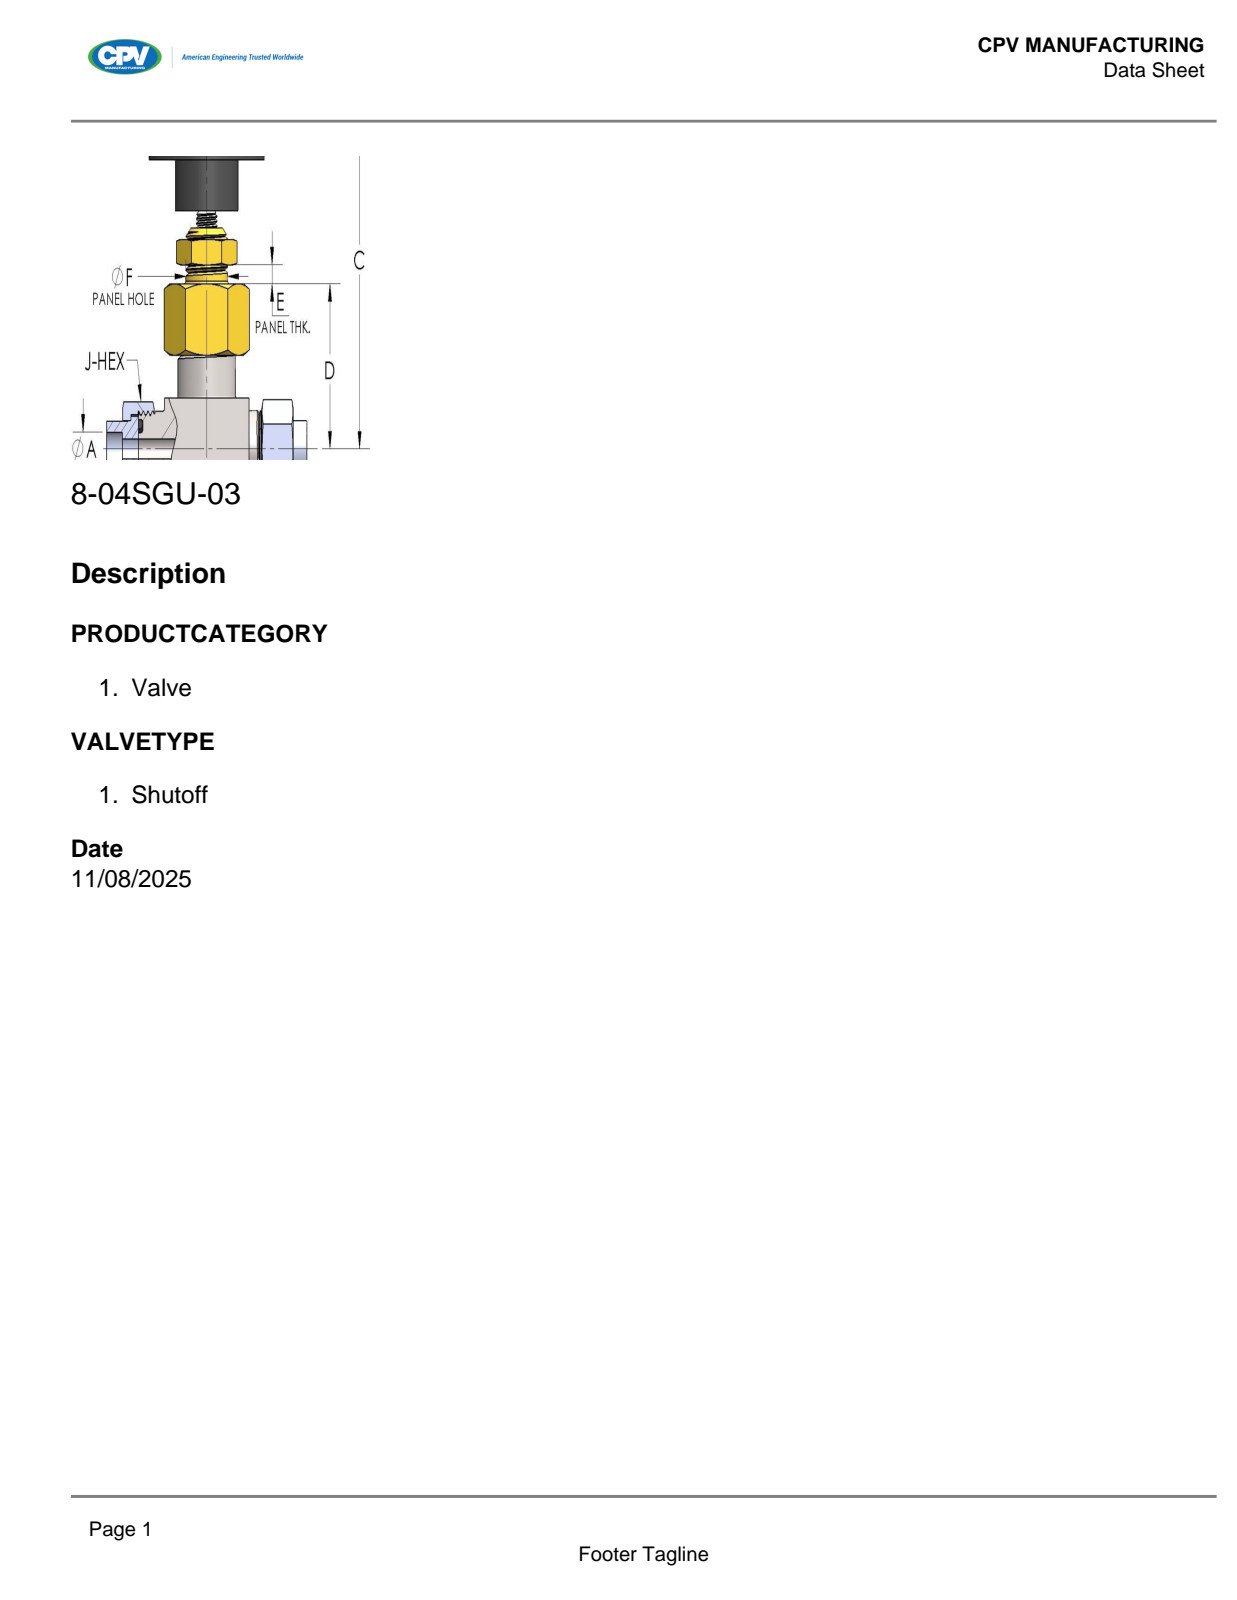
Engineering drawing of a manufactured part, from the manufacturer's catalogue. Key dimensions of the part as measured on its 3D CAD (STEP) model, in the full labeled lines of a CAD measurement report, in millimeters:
Part name (STEP PRODUCT): 8-04SGU-03
STEP written by: SolidWorks 2018 (AUTOMOTIVE_DESIGN)
Units: millimetres
Bodies: 2 solids, 224 faces (65 planar, 60 cylindrical, 99 other)
Overall size (bounding box): 73 × 60.7 × 35.1
Volume: 35 660 mm³ · Surface area: 11 950 mm²
Round holes (diameter × count): ⌀4 ×1, ⌀4.1 ×1, ⌀4.9 ×1, ⌀4.9 ×1
Round bosses / shafts (diameter × count): ⌀4.8 ×2, ⌀35.1 ×1, ⌀19.1 ×1, ⌀17.3 ×1, ⌀14.2 ×1, ⌀12.6 ×1, ⌀8.7 ×1, ⌀6.4 ×1
Main face-to-face distances: 19.1, 8.8, 22.4, 64.2, 73, 16, 13.4, 1.5, 17.5, 9.5
